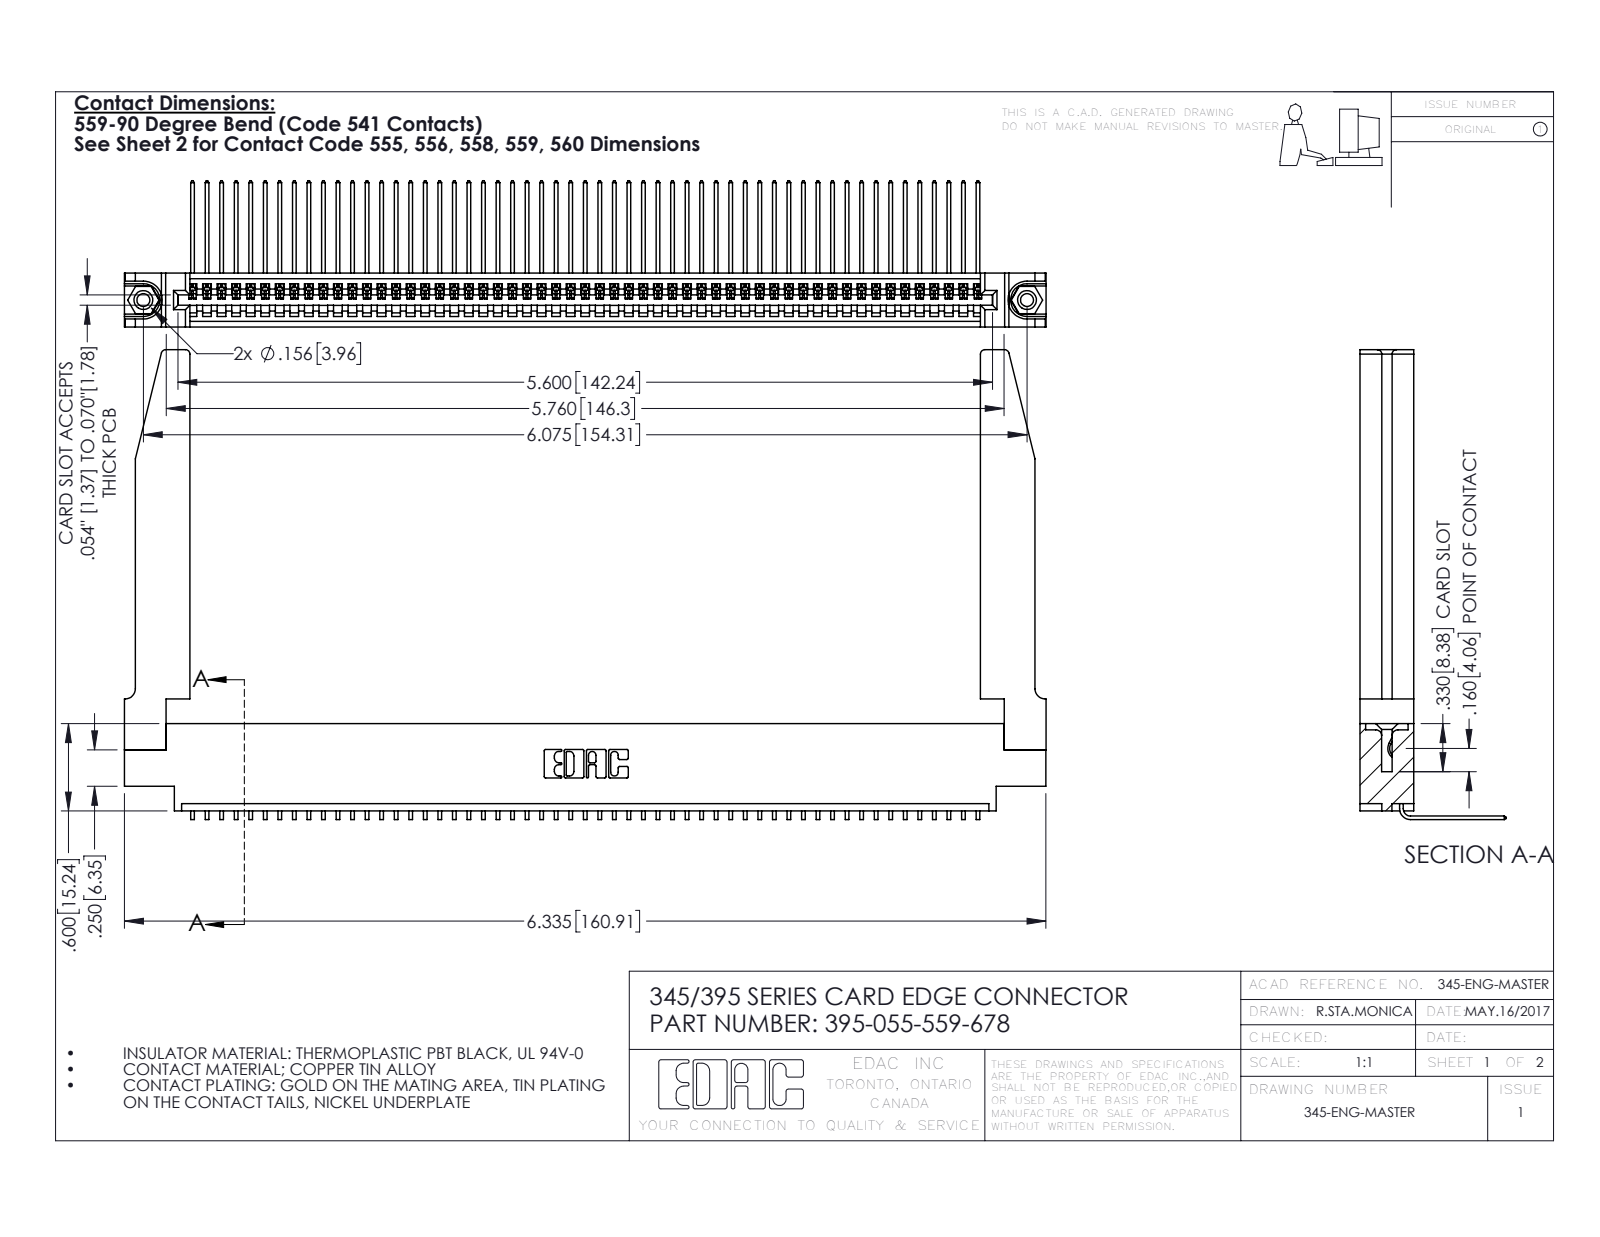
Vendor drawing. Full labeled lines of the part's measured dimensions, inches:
Part name (STEP PRODUCT): 395-055-559-678; 345-220-078_345-220-078; 345-292-001_558 559 Tail - 1; 345-250-001_345-250-001-102 (+1 more)
STEP written by: SolidWorks 2016 (CONFIG_CONTROL_DESIGN)
Units: inches
Bodies: 60 solids, 3664 faces (2536 planar, 1076 cylindrical, 52 other)
Overall size (bounding box): 6.336 × 3.229 × 1.005
Volume: 1.418 in³ · Surface area: 44.6 in²
Round holes (diameter × count): ⌀0.089 ×2, ⌀0.125 ×2, ⌀0.156 ×2, ⌀0.064 ×1
Round bosses / shafts (diameter × count): ⌀0.155 ×2
Partial cylindrical surfaces — rounded edges, fillets, slot ends (radius × count): R0.006 ×110, R0.01 ×22, R0.03 ×8, R0.007 ×6, R0.031 ×6, R0.026 ×3, R0.031 ×2, R0.04 ×2
Main face-to-face distances: 0.37, 0.072, 0.298, 0.098, 0.272, 0.025, 0.2, 0.225, 0.148, 0.15
Hole centre spacings: 0.27, 5.839, 6.075
